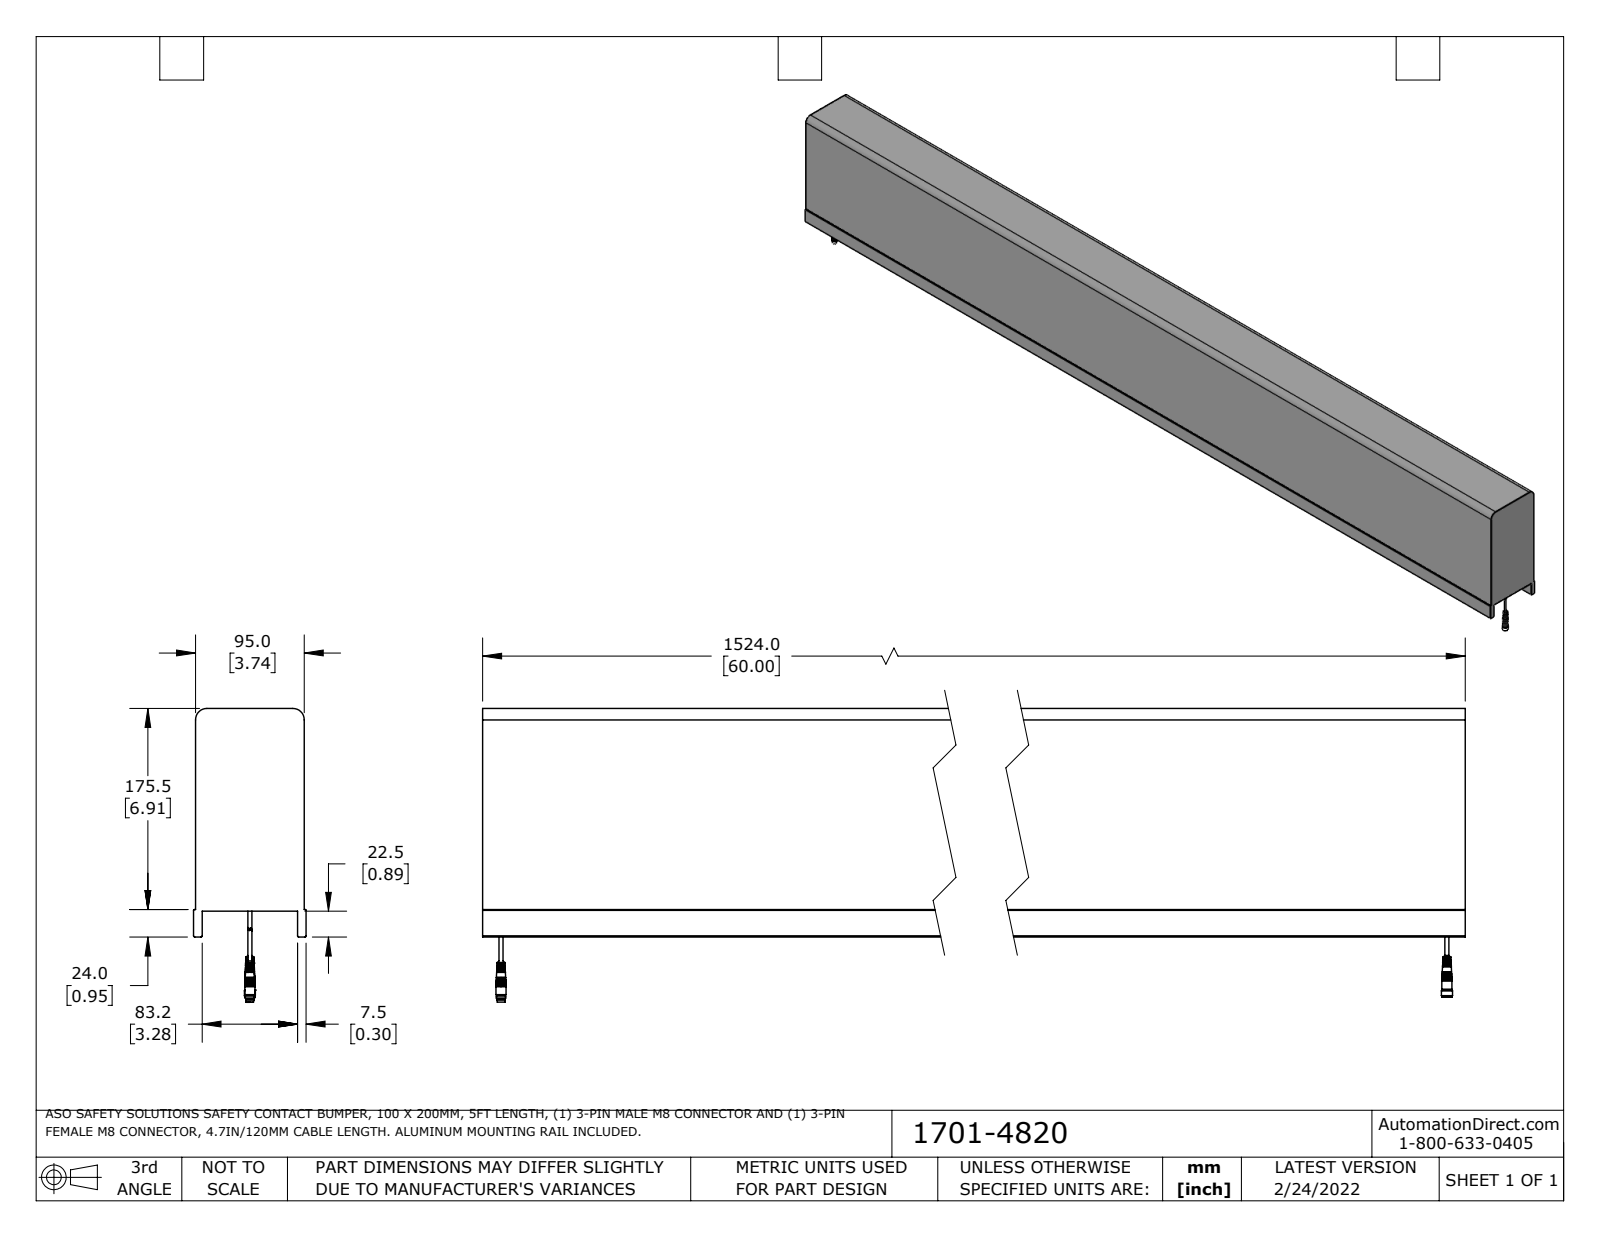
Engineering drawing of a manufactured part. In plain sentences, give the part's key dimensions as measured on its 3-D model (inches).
The part is named "1701-4820_Default". Its 3-D file was written by "SolidWorks 2021 (CONFIG_CONTROL_DESIGN)". It is 24 solids with 447 faces: 175 planar, 154 cylindrical and 118 other. Overall it measures 60 by 10.096 by 3.868 inches. Its volume is 1 592 cubic inches and its surface area 1 551 square inches. Round holes: 4 of diameter 0.047, 3 of diameter 0.033, 3 of diameter 0.063, 2 of diameter 0.134, 1 of diameter 0.228, 1 of diameter 0.232, 1 of diameter 0.272, 1 of diameter 0.283. Round bosses or shafts: 8 of diameter 0.047, 6 of diameter 0.039, 4 of diameter 0.02, 2 of diameter 0.346, 2 of diameter 0.224, 2 of diameter 0.138, 1 of diameter 0.378, 1 of diameter 0.354. Partial cylindrical surfaces (rounded edges, fillets, slot ends): 4 of radius 0.039, 2 of radius 0.03, 2 of radius 0.394. The main face-to-face distances are 3.74, 6.969, 0.064, 3.804, 0.295, 3.572, 0.231, 3.509, 3.868, 3.277. The hole center spacings are 58.74, 0.028, 0.069, 58.671, 58.713, 58.768, 58.809, 0.041.
